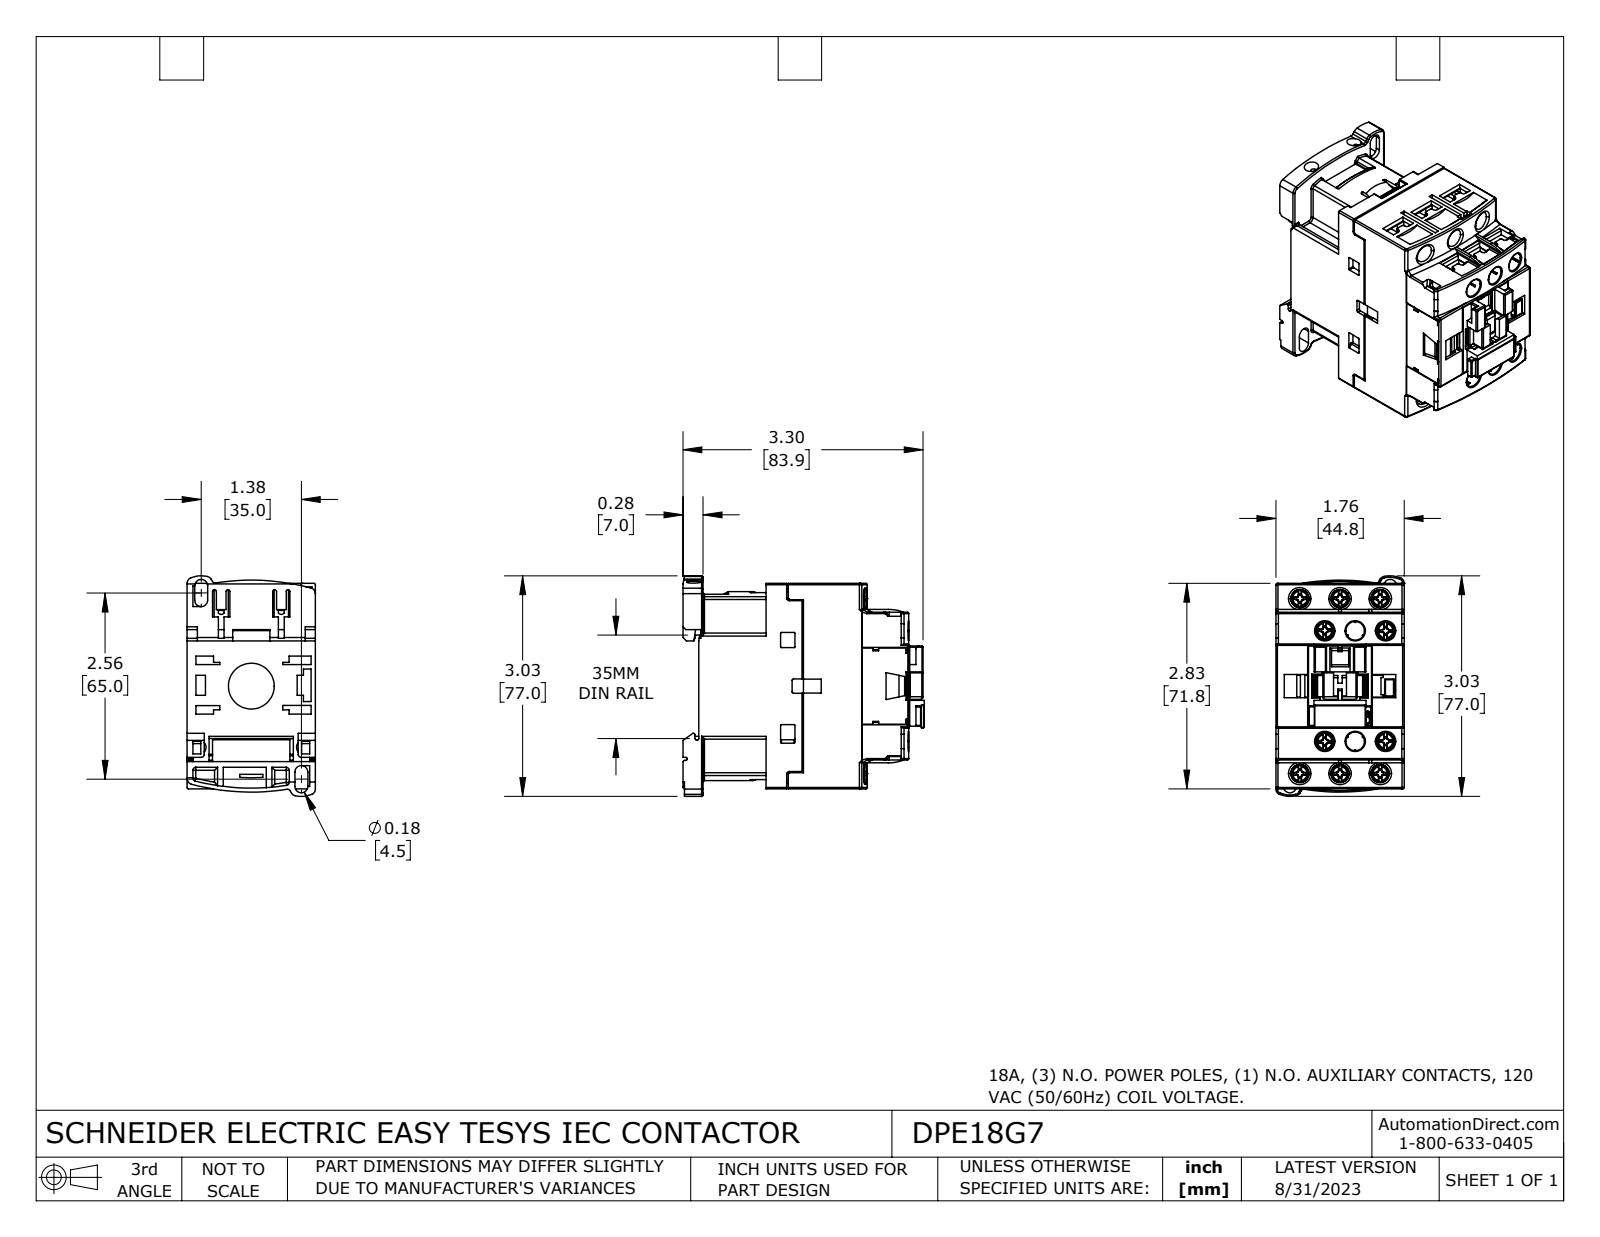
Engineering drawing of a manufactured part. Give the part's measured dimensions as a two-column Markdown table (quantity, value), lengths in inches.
| quantity | value |
| --- | --- |
| part name | DPE18G7 |
| STEP written by | SolidWorks 2021 (CONFIG_CONTROL_DESIGN) |
| units | inches |
| bodies | 20 solids, 3363 faces (2297 planar, 694 cylindrical, 372 other) |
| overall size | 3.317 × 3.031 × 1.783 |
| volume | 8.907 in³ |
| surface area | 103.4 in² |
| round holes (diameter × count) | 0.252 × 6, 0.256 × 6, 0.197 × 2, 0.167 × 1, 0.63 × 1 |
| round bosses / shafts (diameter × count) | 0.138 × 10, 0.108 × 10, 0.315 × 6 |
| partial cylindrical surfaces (radius × count) | 0.02 × 78, 0.012 × 64, 0.039 × 61, 0.006 × 42, 0.016 × 24, 0.63 × 9, 0.024 × 8, 0.079 × 7 |
| main face-to-face distances | 0.047, 1.764, 1.717, 0.321, 1.128, 0.807, 0.35, 2.78, 1.366, 1.118 |
| hole center spacings | 0.417, 0.488, 0.551, 0.558, 0.788, 0.878, 1.321, 1.576 |
